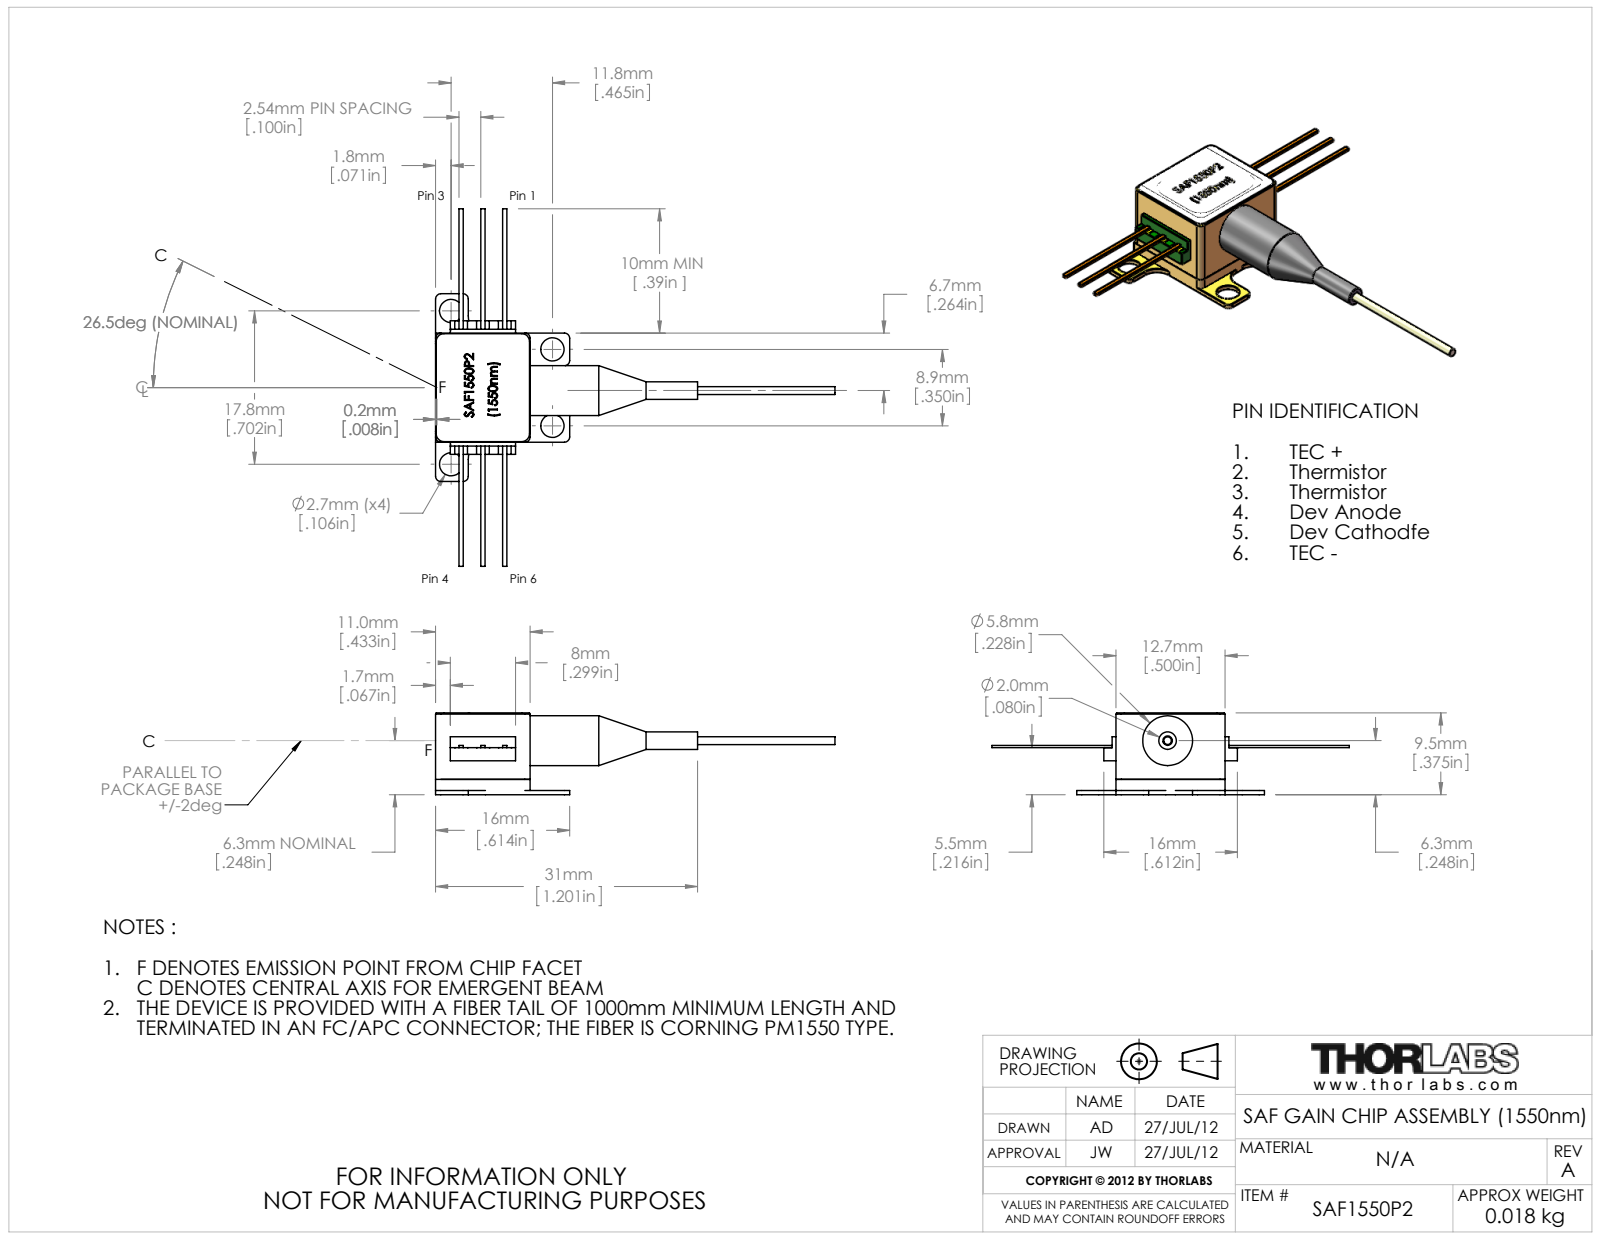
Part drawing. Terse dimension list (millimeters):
name: 24727-E0W
written by: SolidWorks 2011 (AUTOMOTIVE_DESIGN)
unit: mm
bodies: 15 solids, 489 faces (313 planar, 70 cylindrical, 106 other)
size: 46.5 × 41.6 × 9.53
volume: 931 mm³; area: 2 425 mm²
holes: 4× ⌀2.7, 1× ⌀1.1, 1× ⌀2.08, 1× ⌀3.18, 1× ⌀4.1
bosses: 1× ⌀5.8, 1× ⌀3.45, 1× ⌀2.04, 1× ⌀0.9
rounds: 12× R0.6, 10× R1, 4× R0.13, 4× R0.3, 4× R0.9, 4× R1.85, 4× R2
face distances: 1, 1.6, 9.52, 7.92, 7.6, 9.4, 7.8, 1.8, 1.45, 11.7
hole spacings: 12.62, 17.83, 8.9, 17.84
